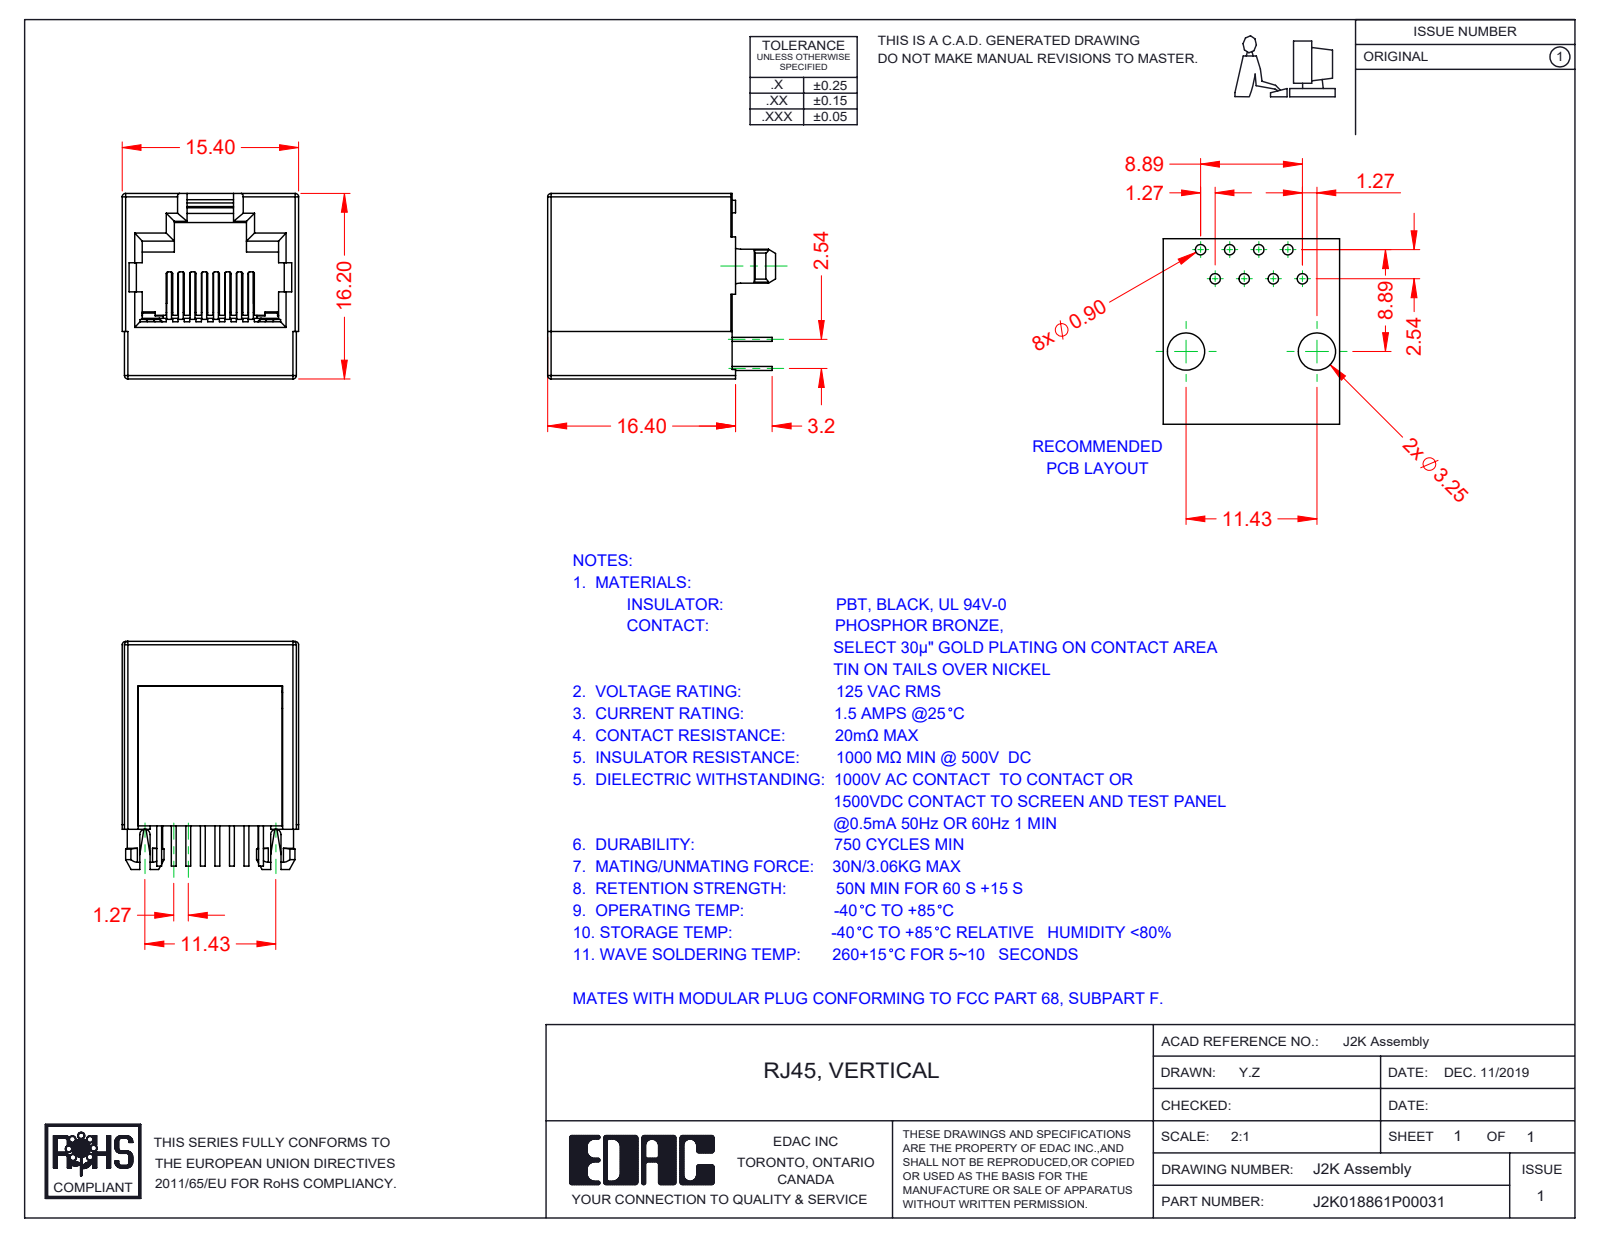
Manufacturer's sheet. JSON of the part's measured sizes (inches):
{"part_name": "2K Contact Lock; 2K Contacts; RJ2K018861P00031; 2K Insulator", "step_written_by": "SolidWorks 2016 (CONFIG_CONTROL_DESIGN)", "units": "inches", "bodies": {"solids": 10, "faces": 723, "planar": 586, "cylindrical": 113, "other": 24}, "overall_size": [0.783, 0.638, 0.606], "volume_in3": 0.151, "surface_area_in2": 6.141, "round_bosses_or_shafts": [[0.122, 2], [0.043, 2]], "partial_cylinders_radius": [[0.006, 16], [0.012, 10], [0.02, 3], [0.004, 2], [0.008, 2], [0.018, 2], [0.024, 2], [0.037, 2]], "face_to_face_distances": [0.638, 0.606, 0.055, 0.551, 0.047, 0.543, 0.598, 0.014, 0.02, 0.591]}
